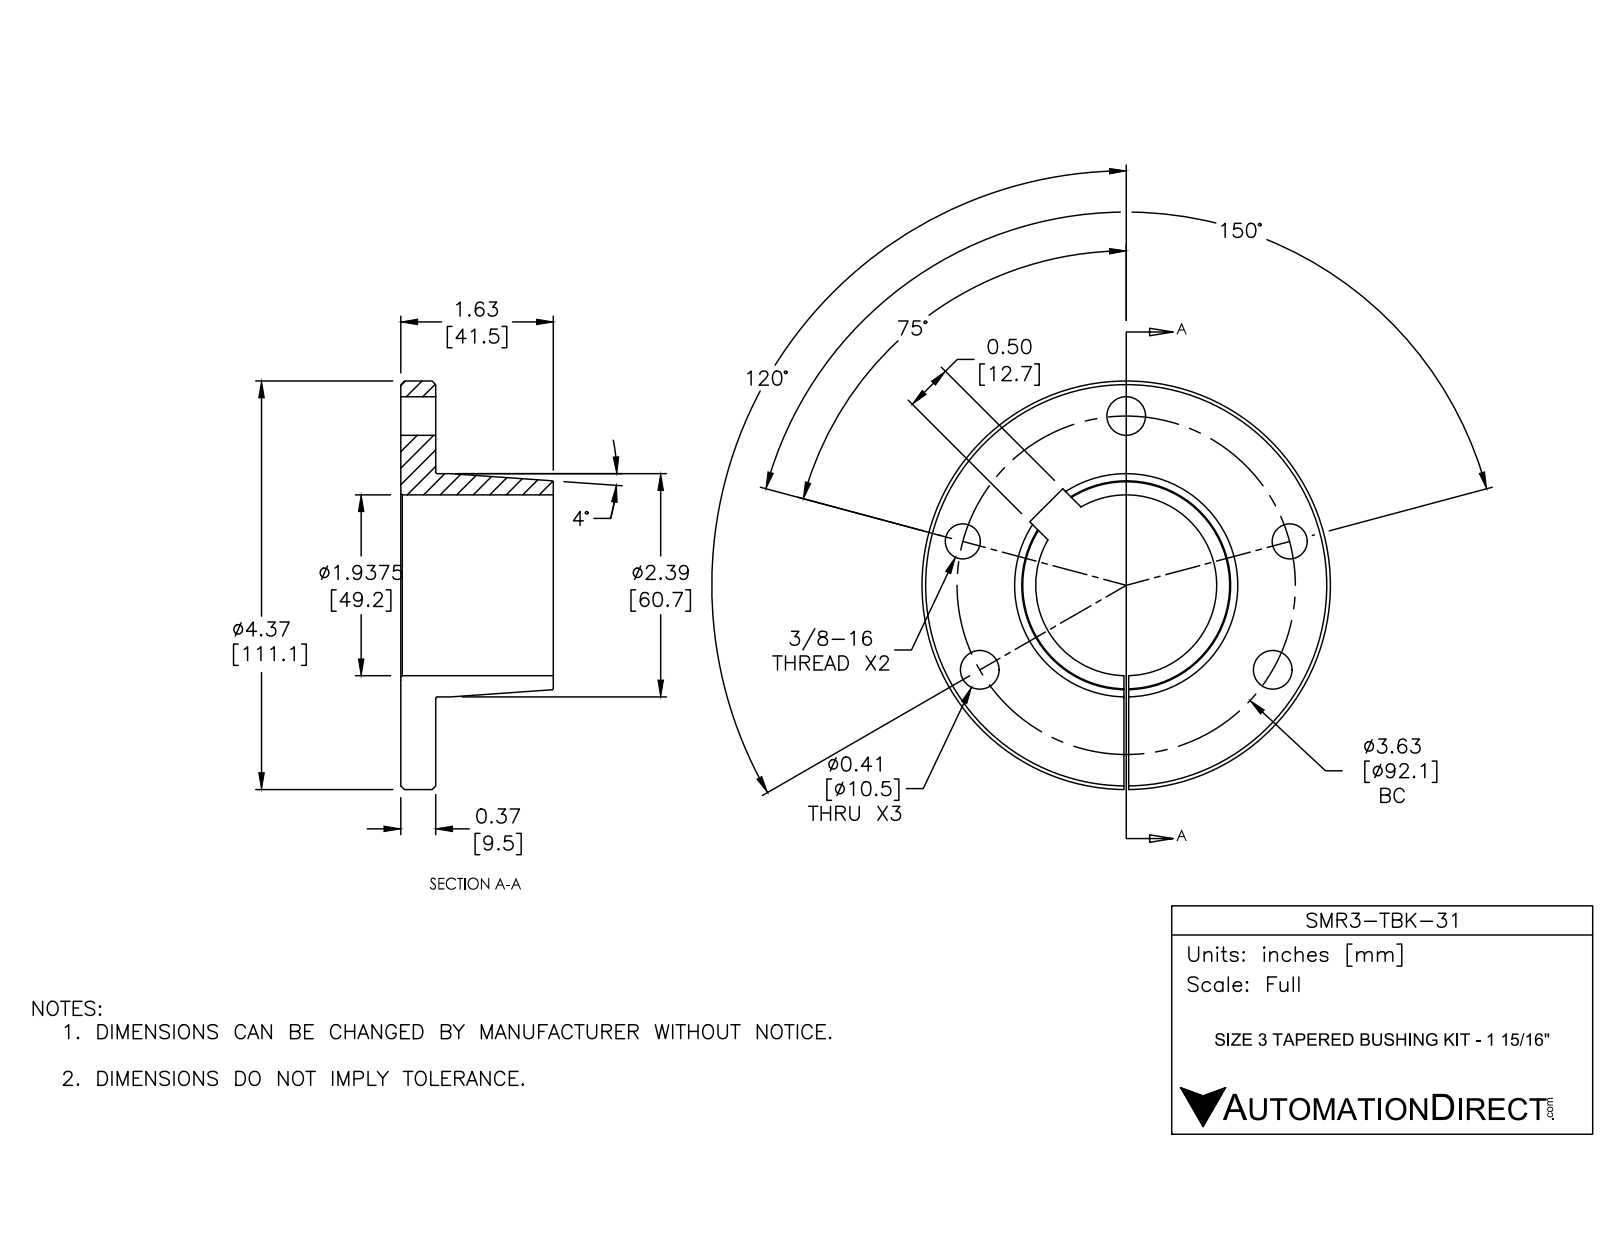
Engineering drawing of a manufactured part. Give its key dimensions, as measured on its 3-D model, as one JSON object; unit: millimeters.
{"part_name": "SMR3-TBK-31", "step_written_by": "SolidWorks 2016 (AUTOMOTIVE_DESIGN)", "units": "millimeters", "bodies": {"solids": 1, "faces": 93, "planar": 9, "cylindrical": 66, "other": 18}, "overall_size": [111.1, 111.1, 41.5], "volume_mm3": 93410, "surface_area_mm2": 31590, "round_holes": [[10.5, 3], [8, 2], [9.5, 2], [49.2, 1]], "round_bosses_or_shafts": [[111.1, 1], [60.7, 1]], "face_to_face_distances": [9.5, 41.5, 32, 1.3, 12.7], "hole_center_spacings": [46.1, 79.7, 35.2, 56.1, 91.3, 89]}
